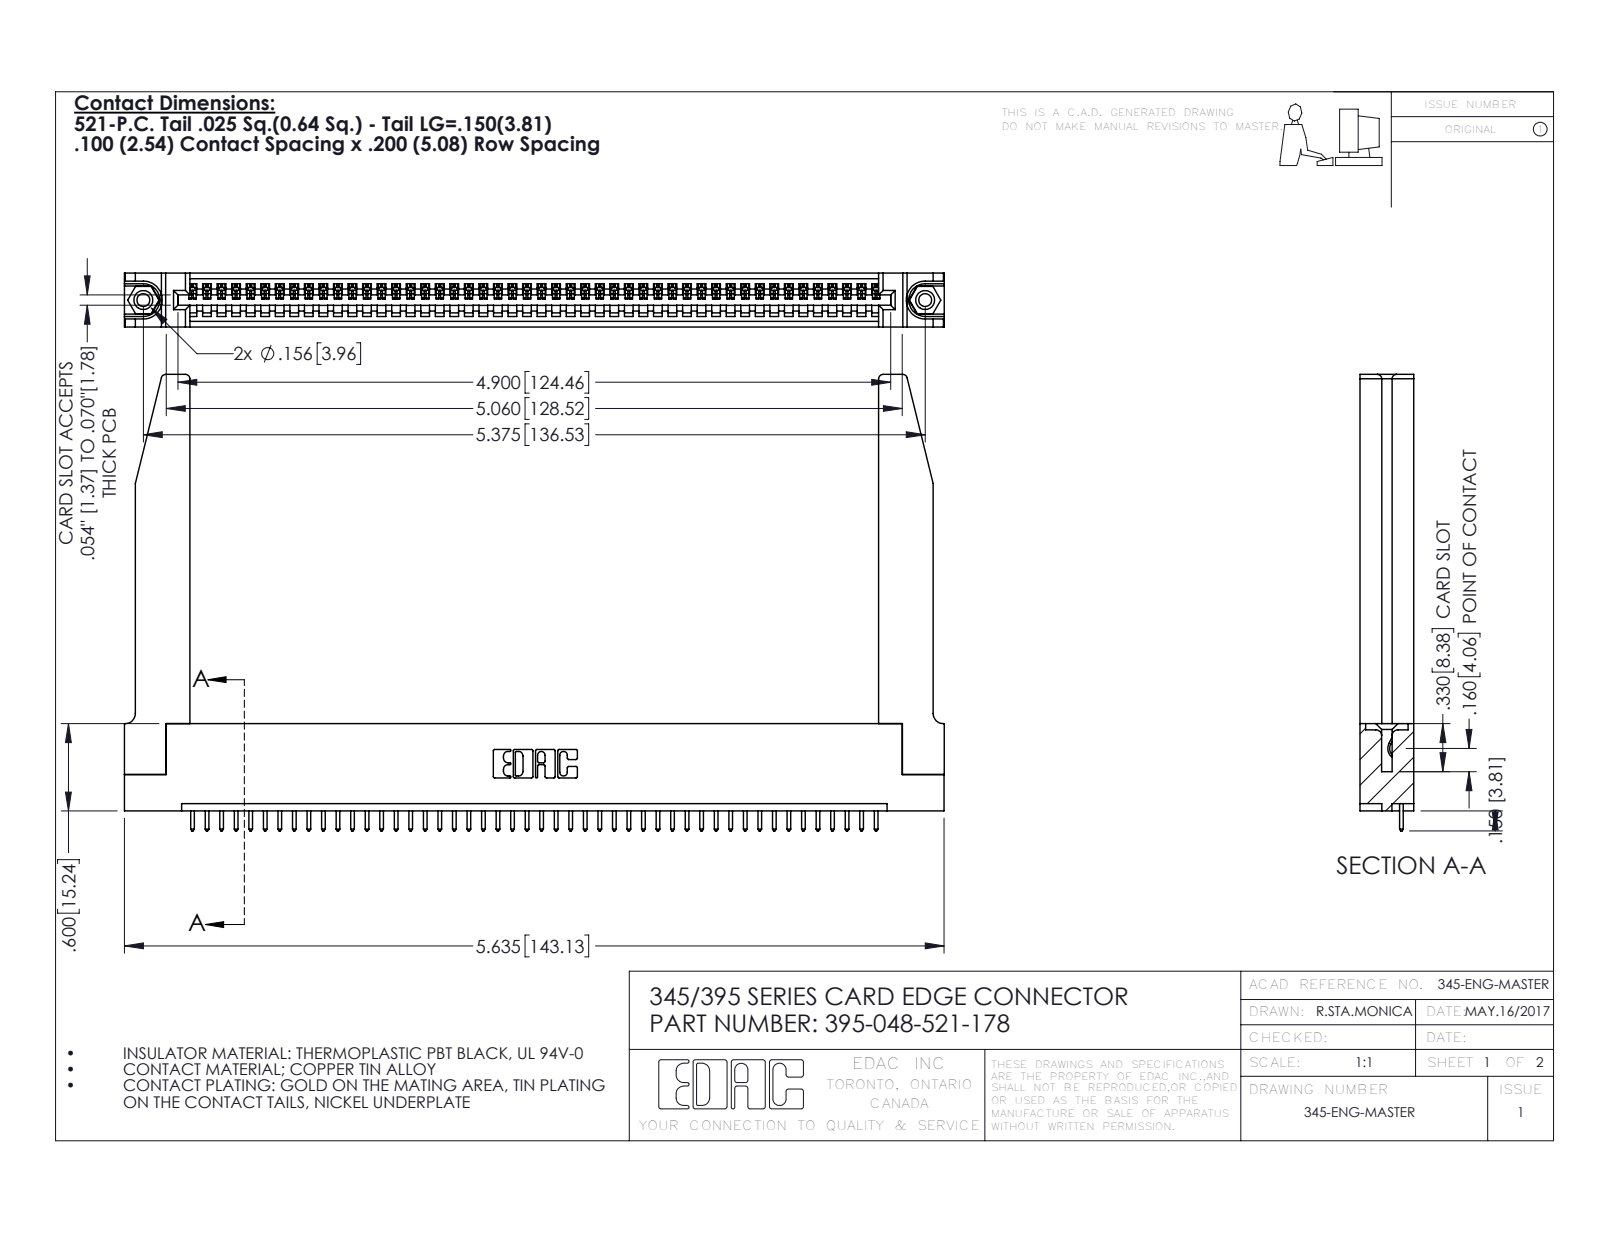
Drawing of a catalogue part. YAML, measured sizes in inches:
part_name: "345 Part_Flush Mounting Lugs - 0.156 Dia-TH; 345-250-001_345-250-001-102; 395-048-521-178; 345-292-001_345-293-121 (+1 more)"
step_written_by: "SolidWorks 2016 (CONFIG_CONTROL_DESIGN)"
units: inches
bodies: {solids: 53, faces: 3144, planar: 2142, cylindrical: 950, other: 52}
overall_size: [5.636, 3.137, 0.37]
volume: 1.299
surface_area: 37.74
round_holes:
  - {diameter: 0.089, count: 2}
  - {diameter: 0.125, count: 2}
  - {diameter: 0.156, count: 2}
  - {diameter: 0.064, count: 1}
round_bosses_or_shafts:
  - {diameter: 0.155, count: 2}
partial_cylinders:
  - {radius: 0.006, count: 96}
  - {radius: 0.01, count: 96}
  - {radius: 0.01, count: 22}
  - {radius: 0.03, count: 8}
  - {radius: 0.007, count: 6}
  - {radius: 0.031, count: 6}
  - {radius: 0.026, count: 3}
  - {radius: 0.031, count: 2}
face_to_face_distances: [0.37, 0.072, 0.298, 0.2, 0.098, 0.272, 0.025, 0.225, 0.15, 0.148]
hole_center_spacings: [0.27, 5.139, 5.375]
